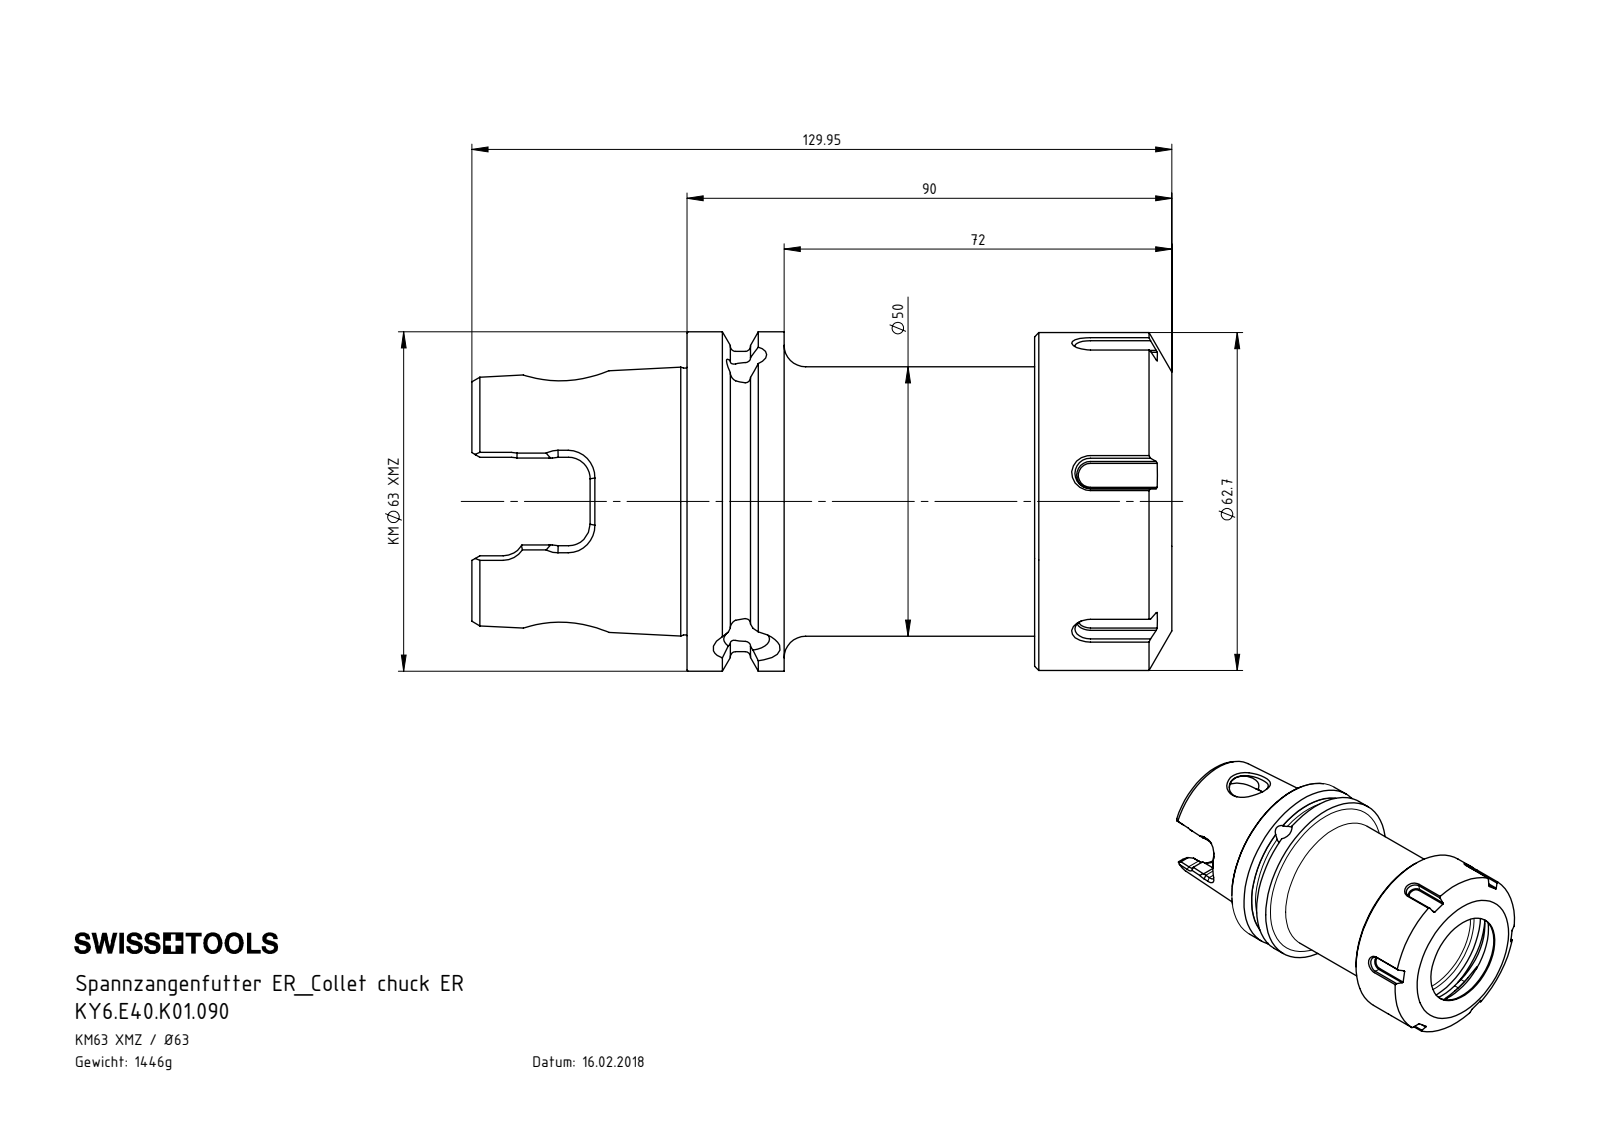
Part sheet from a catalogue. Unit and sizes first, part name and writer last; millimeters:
Units: millimetres
Overall size (bounding box): 129.95 × 62.95 × 62.95
Round holes (diameter × count): ⌀7.47 ×2, ⌀8 ×1, ⌀8.48 ×1, ⌀10 ×1, ⌀11.5 ×1, ⌀14.5 ×1, ⌀31 ×1, ⌀31.1 ×1, ⌀33.5 ×1, ⌀35.27 ×1, ⌀36.5 ×1, ⌀48.5 ×1
Round bosses / shafts (diameter × count): ⌀62.95 ×1, ⌀62.7 ×1, ⌀55.7 ×1, ⌀50 ×1
Partial cylindrical surfaces — rounded edges, fillets, slot ends (radius × count): R4 ×6, R7.04 ×2, R19.26 ×2, R21.25 ×1
Main face-to-face distances: 25.5, 64.5, 90, 80.4, 15.9, 9.6, 1.1, 65.6, 81.5, 91.1
Volume: 184 179 mm³ · Surface area: 45 364 mm²
Bodies: 2 solids, 305 faces (96 planar, 64 cylindrical, 145 other)
Part name (STEP PRODUCT): KY6-E40.K01.090_B; E40-ER1.001.025; KY6.E40.K01.090
STEP written by: SolidWorks 2017 (CONFIG_CONTROL_DESIGN)
